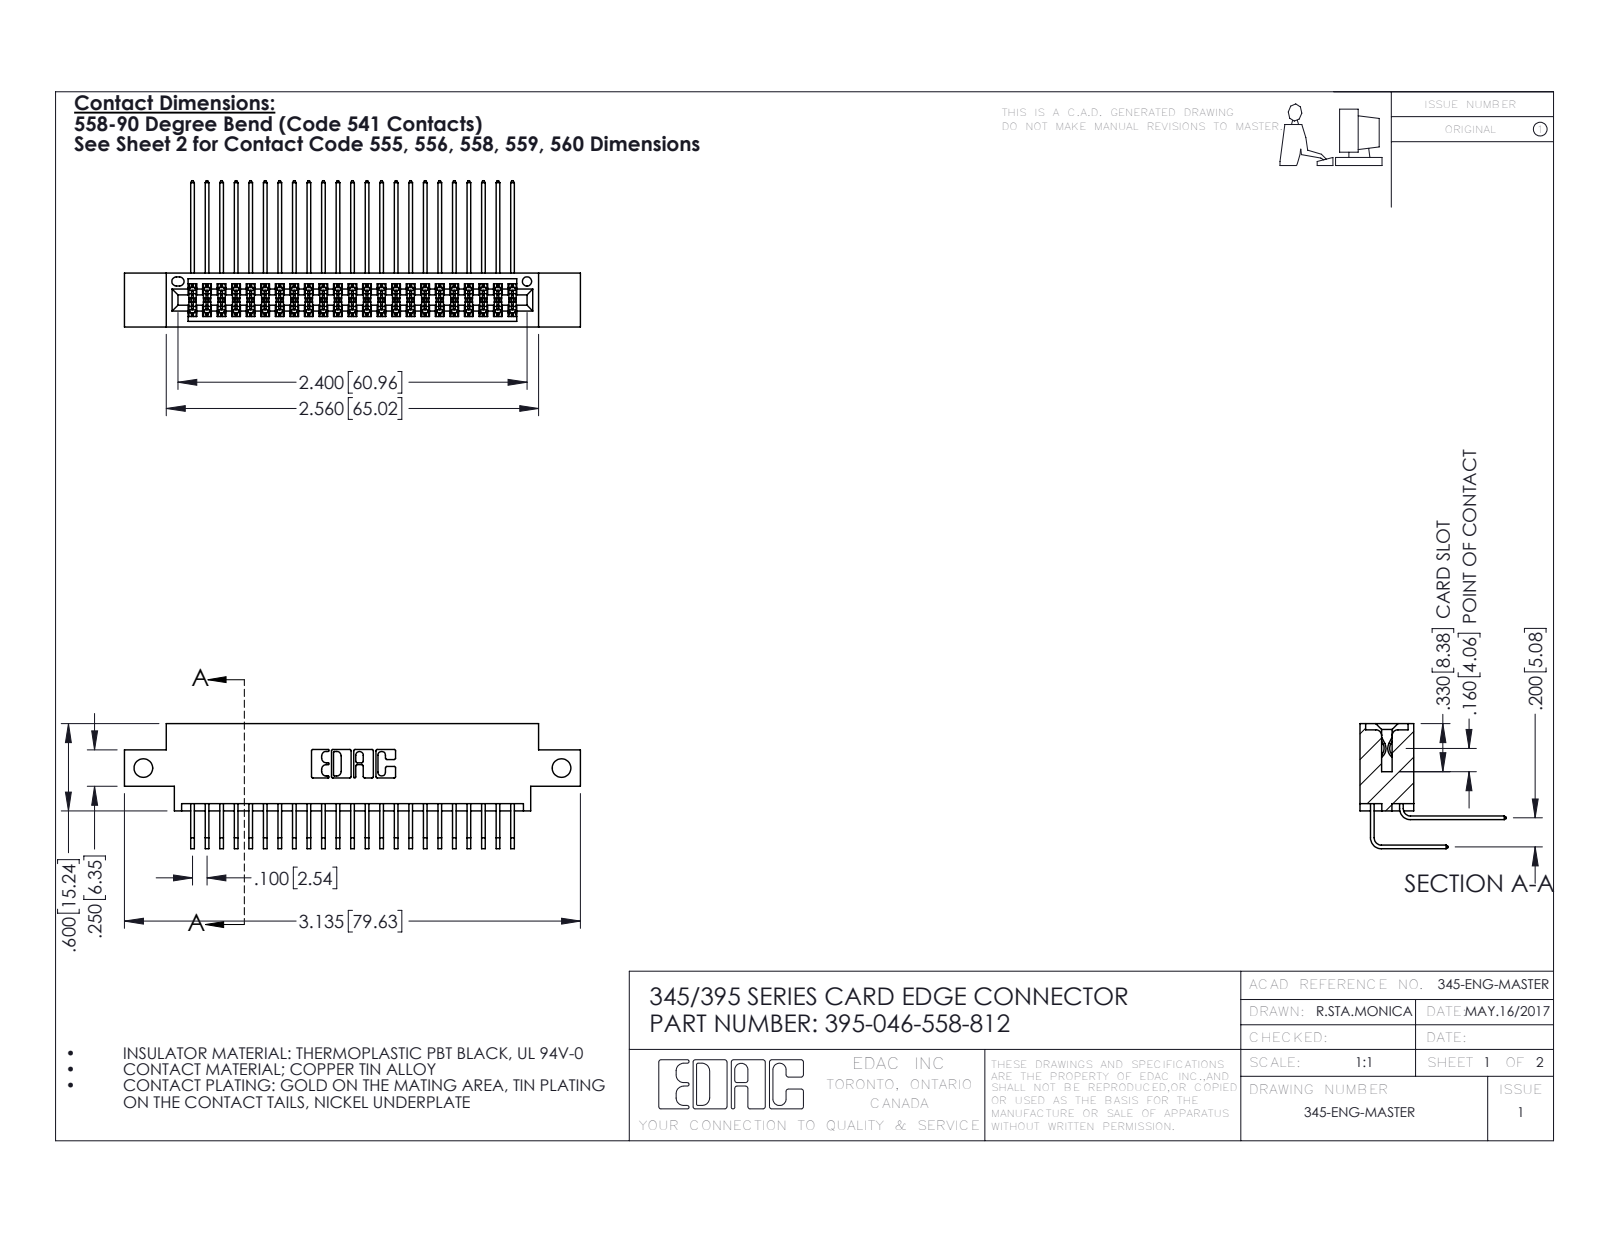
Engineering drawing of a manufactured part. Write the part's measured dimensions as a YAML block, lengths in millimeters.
part_name: "345 Part_0.170 Offset - Side Mount; 345-292-001_558 559 Tail - 1; 395-046-558-812; 345-292-001_558 Tail - 2"
step_written_by: "SolidWorks 2016 (CONFIG_CONTROL_DESIGN)"
units: millimeters
bodies: {solids: 47, faces: 2522, planar: 1694, cylindrical: 828, other: 0}
overall_size: [79.6, 25.5, 21.8]
volume: 7620
surface_area: 12150
round_holes:
  - {diameter: 3.3, count: 2}
  - {diameter: 1.6, count: 1}
partial_cylinders:
  - {radius: 0.2, count: 70}
  - {radius: 0.3, count: 22}
  - {radius: 0.2, count: 6}
  - {radius: 0.8, count: 6}
  - {radius: 0.7, count: 3}
  - {radius: 0.4, count: 2}
  - {radius: 0.5, count: 2}
  - {radius: 0.6, count: 2}
face_to_face_distances: [1.8, 7.6, 5.1, 9.4, 2.5, 6.9, 0.6, 5.7, 4.4, 0.6]
hole_center_spacings: [73]
